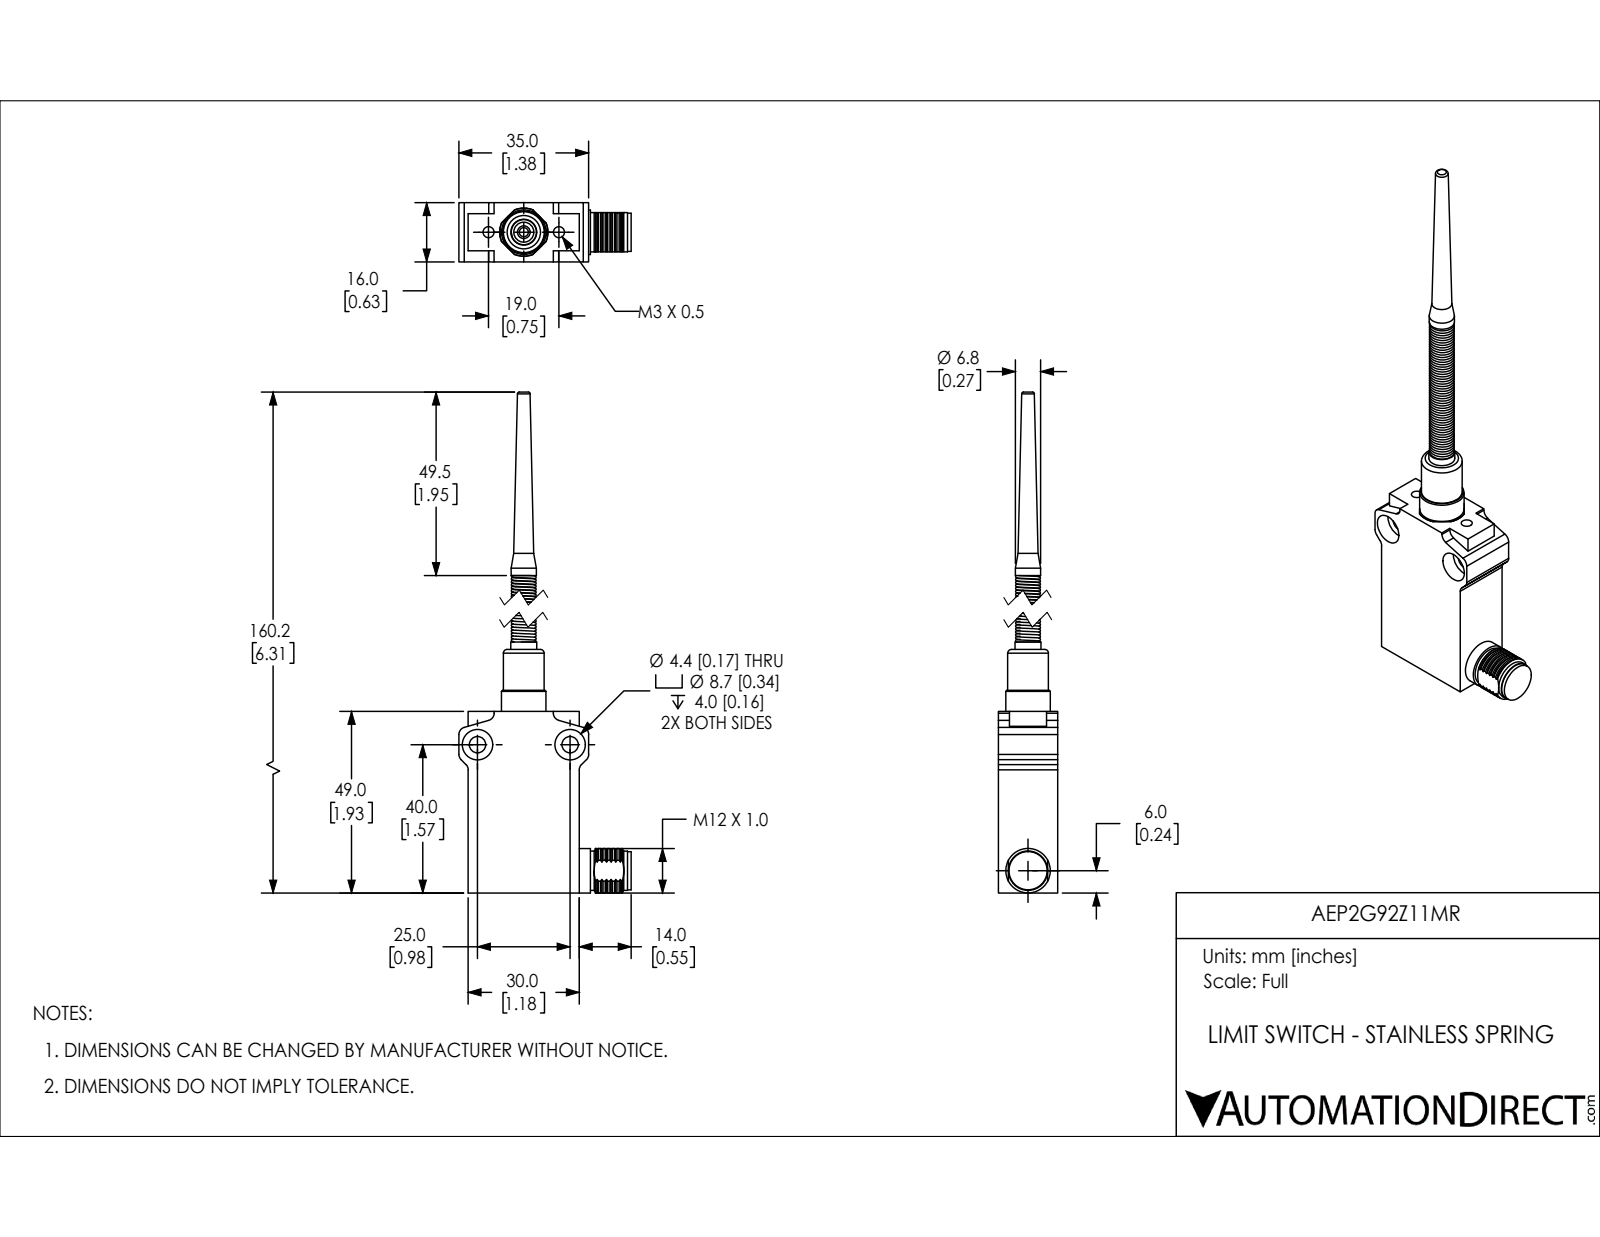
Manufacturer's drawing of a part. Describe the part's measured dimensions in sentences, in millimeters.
The part is named "AEP2G92Z11MR". Its 3-D file was written by "SolidWorks 2018 (AUTOMOTIVE_DESIGN)". It is 5 solids with 202 faces: 57 planar, 86 cylindrical and 59 other. Overall it measures 160.2 by 46.5 by 16 millimeters. Its volume is 27 330 cubic millimeters and its surface area 11 300 square millimeters. Round holes: 2 of diameter 3, 2 of diameter 4.4, 2 of diameter 8.2. Round bosses or shafts: 2 of diameter 12, 1 of diameter 11, 1 of diameter 10.6, 1 of diameter 10.3, 1 of diameter 7, 1 of diameter 6.8. Partial cylindrical surfaces (rounded edges, fillets, slot ends): 8 of radius 2, 1 of radius 6.5. The main face-to-face distances are 16, 30, 49, 12, 44.2, 4.8, 2.5, 32.5, 4, 3. The hole center spacings are 19, 25.
